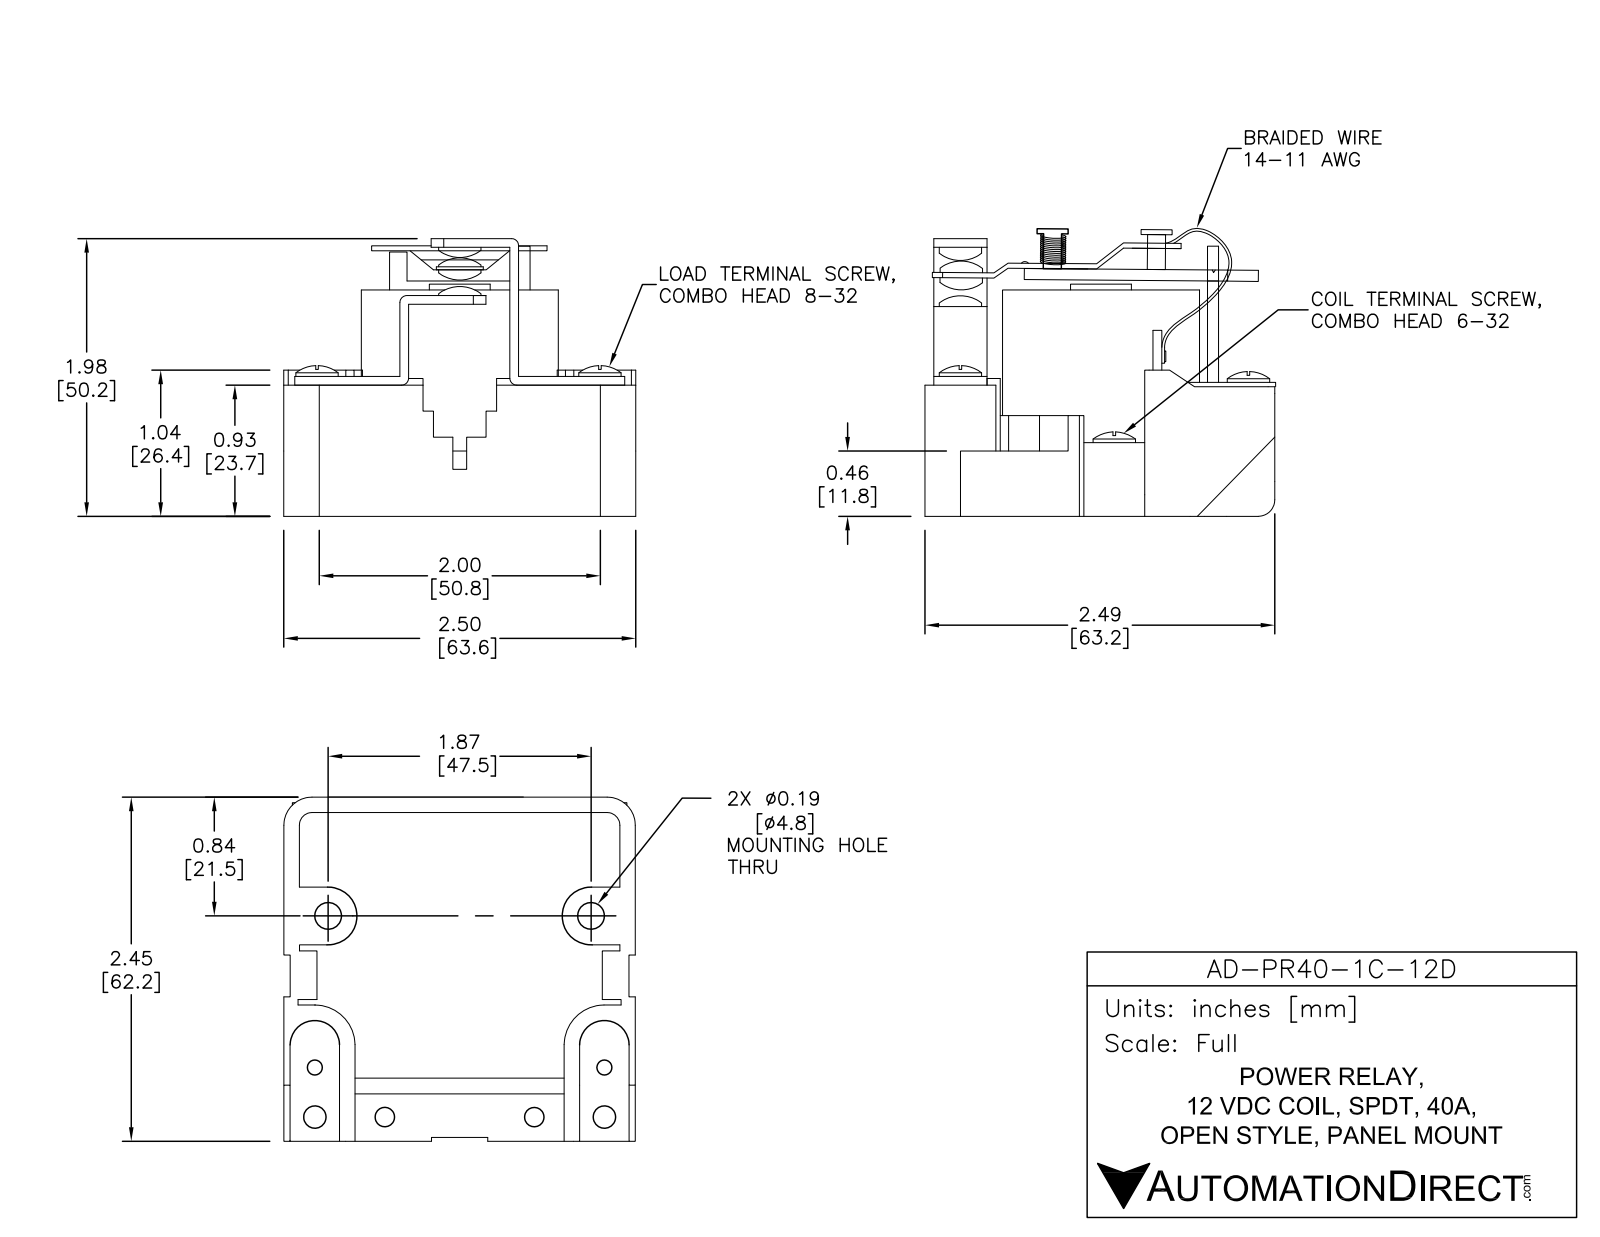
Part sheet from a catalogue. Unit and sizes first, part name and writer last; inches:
Units: inches
Overall size (bounding box): 2.557 × 2.524 × 2.03
Round holes (diameter × count): ⌀0.197 ×4, ⌀0.098 ×2, ⌀0.131 ×2, ⌀0.394 ×2, ⌀1.181 ×1
Round bosses / shafts (diameter × count): ⌀0.305 ×3, ⌀0.27 ×2, ⌀0.208 ×2, ⌀1.398 ×1, ⌀0.709 ×1, ⌀0.394 ×1, ⌀0.256 ×1, ⌀0.217 ×1
Partial cylindrical surfaces — rounded edges, fillets, slot ends (radius × count): R0.03 ×10, R0.118 ×6, R0.015 ×4, R0.039 ×4, R0.058 ×4, R0.059 ×4, R0.079 ×3, R0.02 ×2
Main face-to-face distances: 0.472, 0.079, 0.394, 2.52, 1.289, 0.069, 0.039, 0.059, 1.211, 0.256
Hole centre spacings: 0.394, 1.031, 1.083, 1.178, 1.439, 1.477, 1.939, 1.978
Volume: 5.555 in³ · Surface area: 51.82 in²
Bodies: 34 solids, 625 faces (406 planar, 128 cylindrical, 91 other)
Part name (STEP PRODUCT): AD-PR40-1C-12D
STEP written by: SolidWorks 2013 (AUTOMOTIVE_DESIGN)
